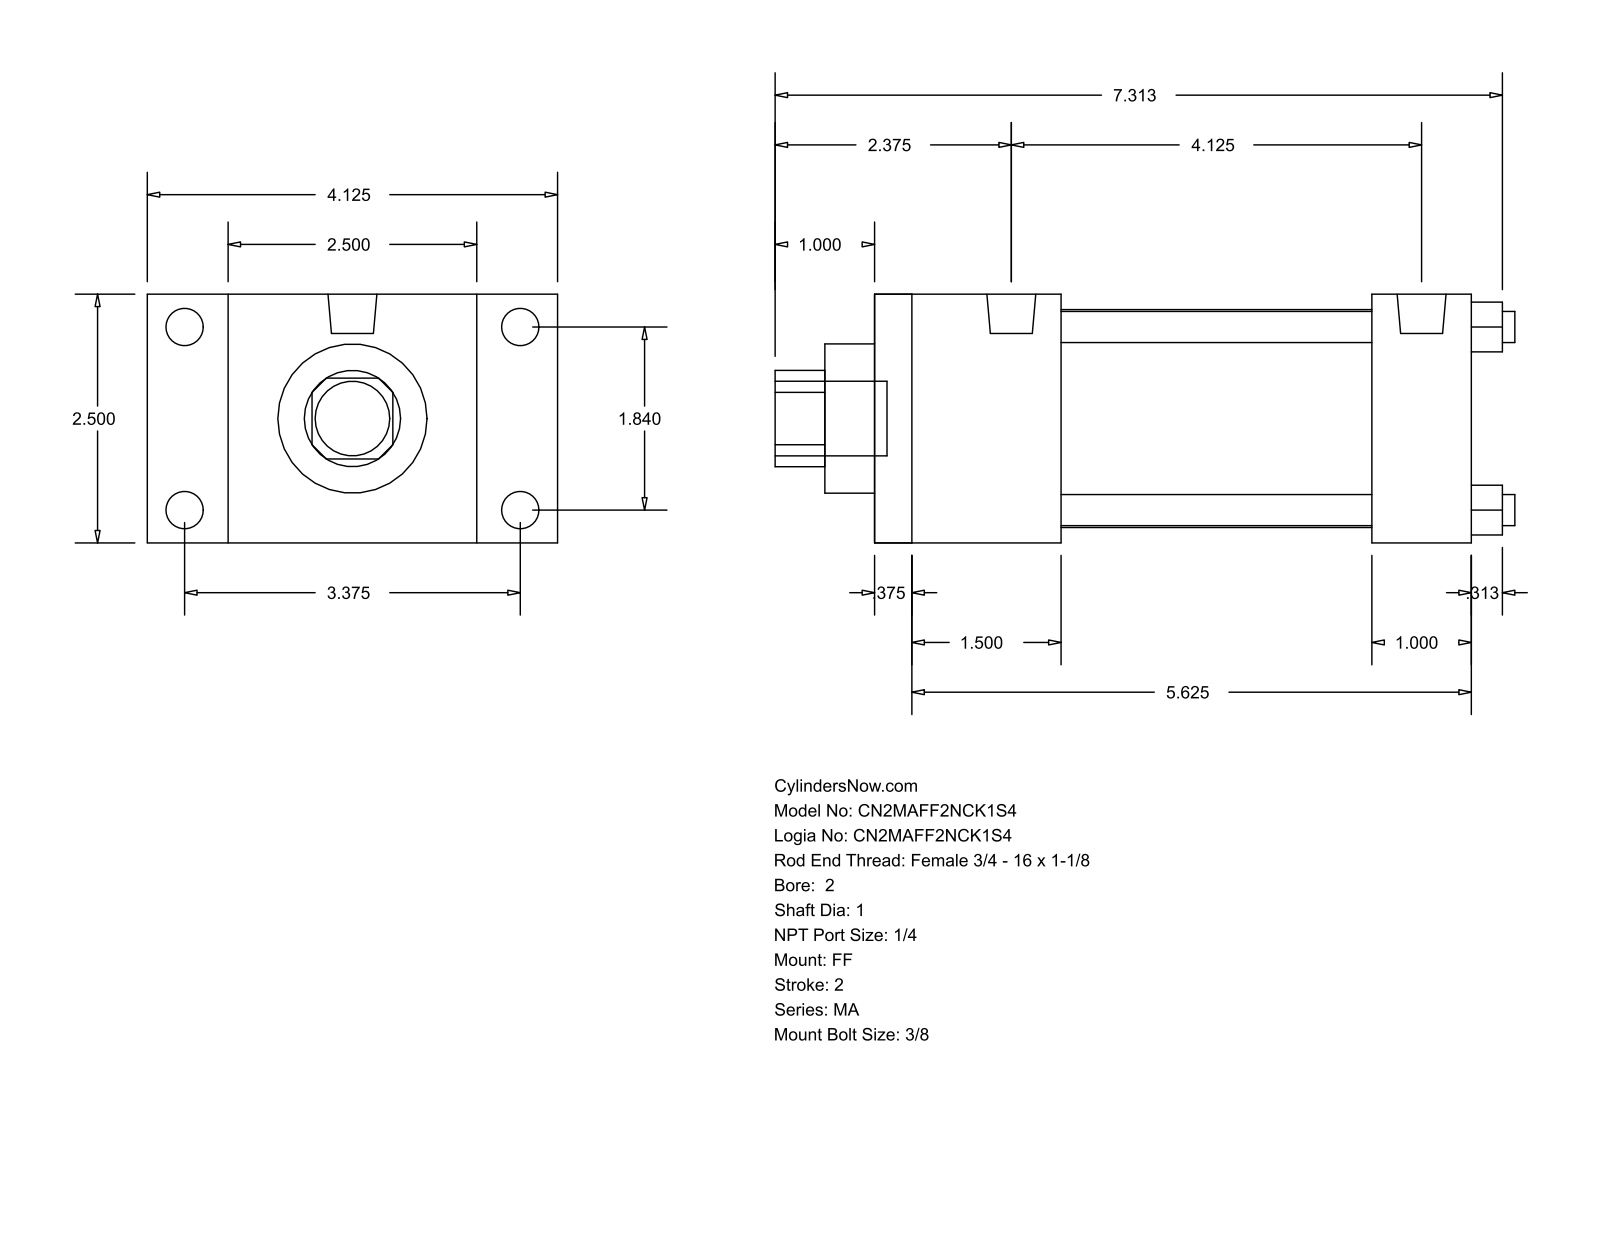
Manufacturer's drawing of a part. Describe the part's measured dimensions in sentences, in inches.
The part is named "MA_FF__0200_1". Its 3-D file was written by "GSSL Pune (CONFIG_CONTROL_DESIGN)". It is 0 solids with 92 faces: 64 planar, 28 cylindrical and 0 other. Overall it measures 7.437 by 4.125 by 2.5 inches. Round holes: 4 of diameter 0.313, 1 of diameter 1, 1 of diameter 1.5, 1 of diameter 2.19. Round bosses or shafts: 4 of diameter 0.375, 4 of diameter 0.313, 2 of diameter 0.492, 1 of diameter 0.75. Partial cylindrical surfaces (rounded edges, fillets, slot ends): 1 of radius 0.484. The main face-to-face distances are 2.5, 6, 0.375, 5.625, 1, 0.813, 0.5, 1.875, 5, 1.5. The hole center spacings are 1.301, 1.84, 2.602.
